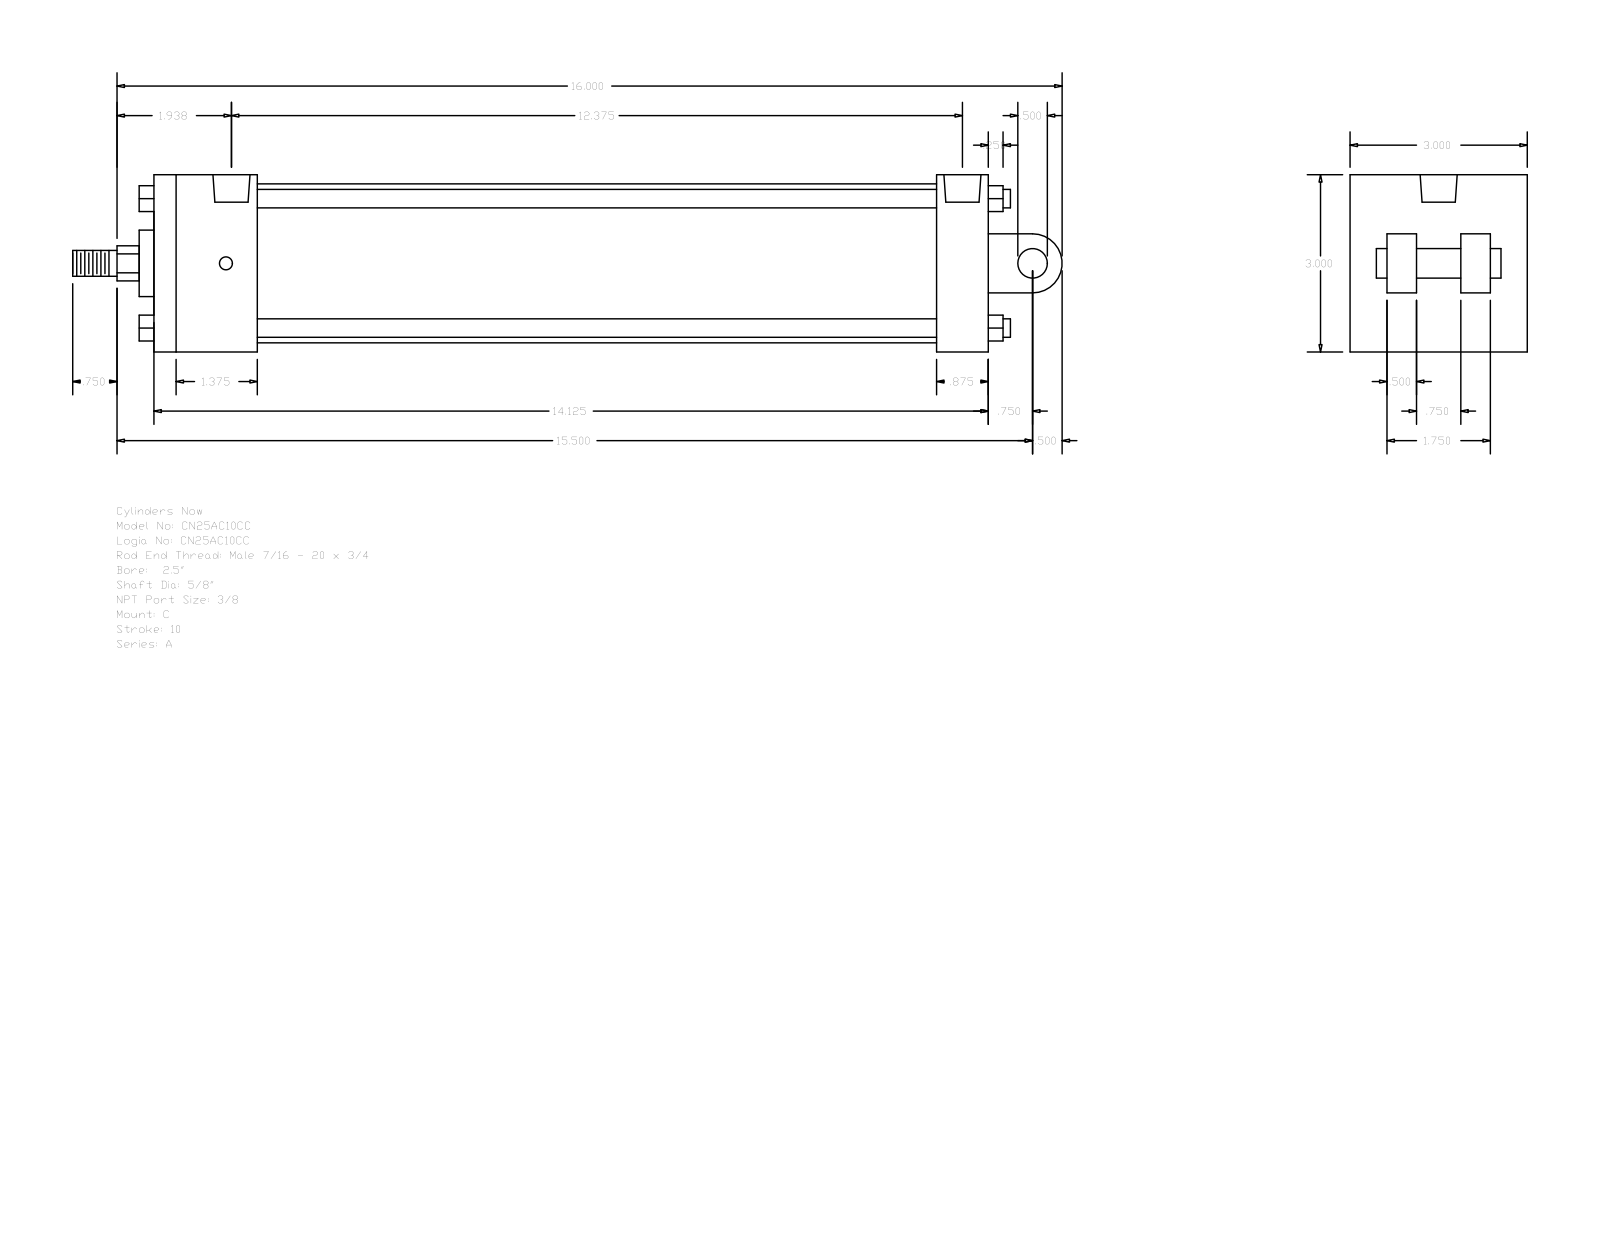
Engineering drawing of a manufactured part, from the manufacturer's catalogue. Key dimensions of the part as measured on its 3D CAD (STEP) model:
Part name (STEP PRODUCT): A_C__0250_0.625
STEP written by: GSSL Pune (CONFIG_CONTROL_DESIGN)
Units: millimetres
Bodies: 0 solids, 135 faces (102 planar, 33 cylindrical, 0 other)
Overall size (bounding box): 425.45 × 76.2 × 76.2
Round holes (diameter × count): ⌀5.56 ×4, ⌀15.93 ×2
Round bosses / shafts (diameter × count): ⌀7.94 ×4, ⌀68.33 ×1, ⌀28.57 ×1, ⌀15.88 ×1, ⌀12.7 ×1, ⌀11.11 ×1
Partial cylindrical surfaces — rounded edges, fillets, slot ends (radius × count): R7.54 ×1, R12.7 ×1
Main face-to-face distances: 76.2, 358.77, 44.45, 336.55, 292.1, 314.32, 22.22, 50.8, 12.7, 25.4
Hole centre spacings: 2.38, 316.71, 319.09, 314.33
